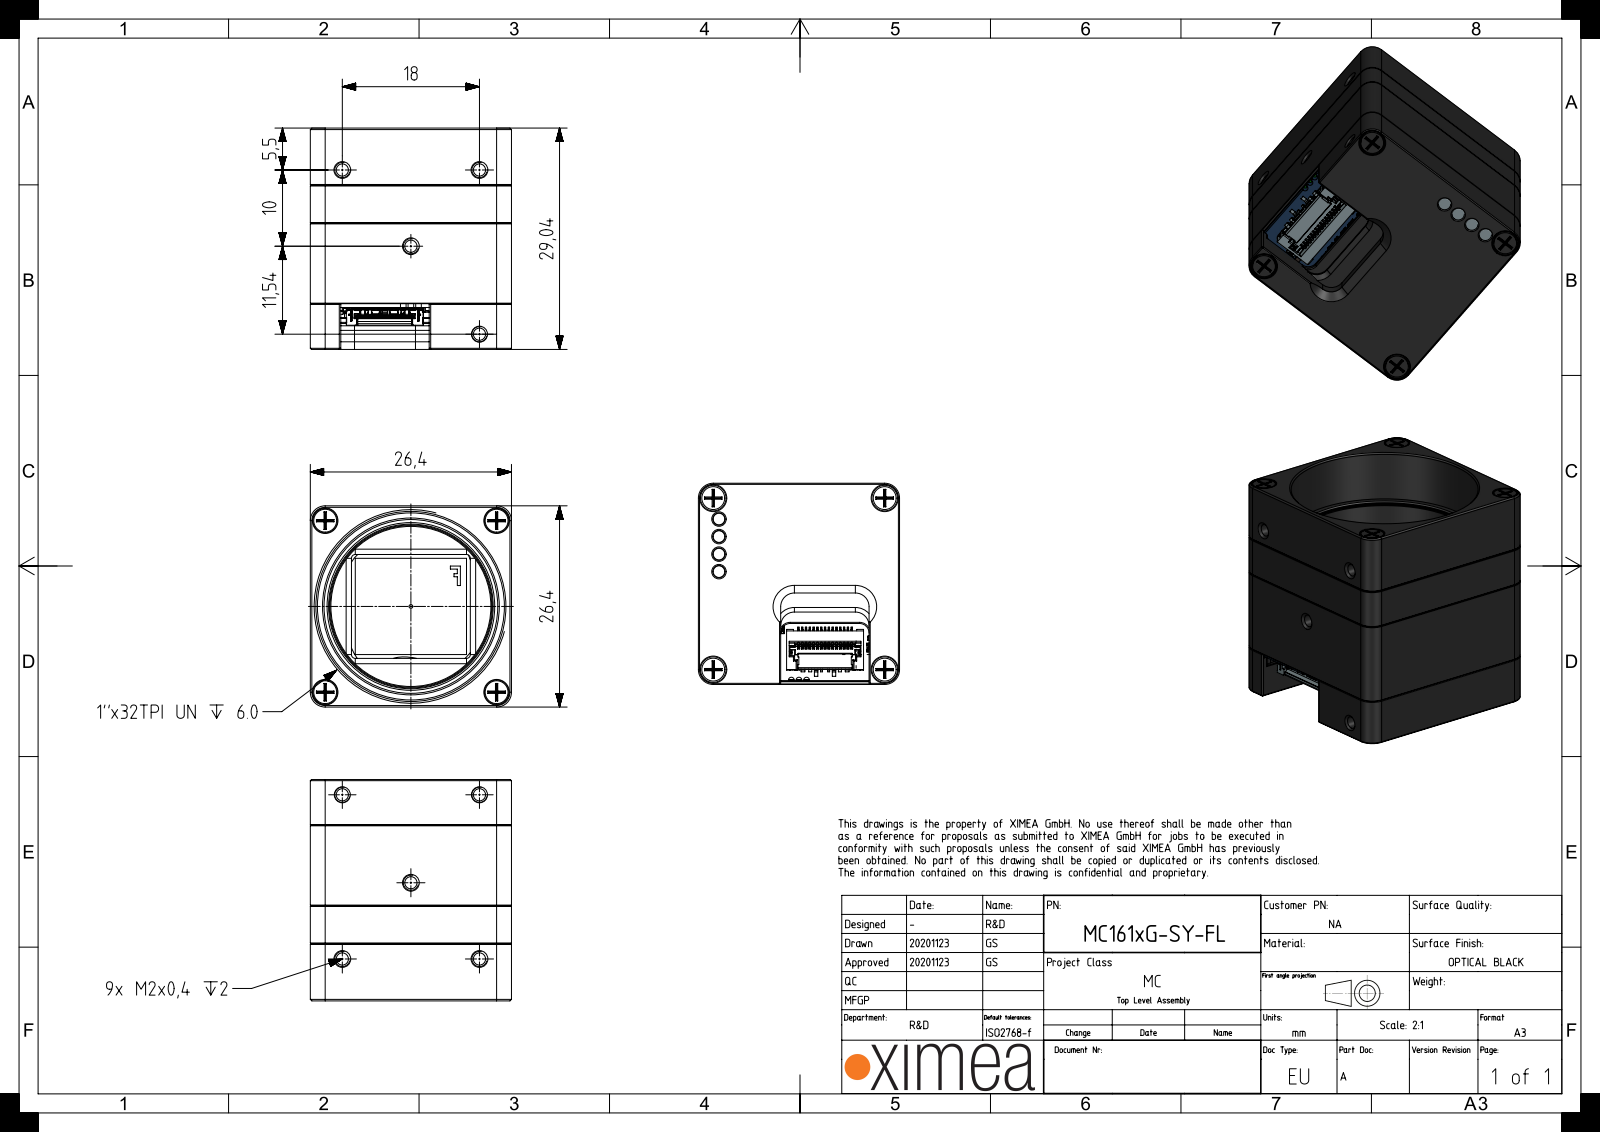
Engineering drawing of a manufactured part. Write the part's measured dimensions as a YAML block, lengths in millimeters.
part_name: "MT160xG-PR-SENSOR-PCA-LW; MECH-CB262-ANTIDUST-GSKT; MECH-O-RING-22X1-VI370; FLT-BK7-AR2X-D25 (+8 more)"
step_written_by: "SIEMENS PLM Software NX 1907 (AUTOMOTIVE_DESIGN)"
units: millimeters
bodies: {solids: 31, faces: 6735, planar: 4771, cylindrical: 1682, other: 282}
overall_size: [29, 26.4, 26.4]
volume: 9770
surface_area: 17190
round_holes:
  - {diameter: 1.6, count: 13}
  - {diameter: 1, count: 4}
  - {diameter: 2, count: 4}
  - {diameter: 2.1, count: 4}
  - {diameter: 3, count: 4}
  - {diameter: 3.2, count: 4}
  - {diameter: 3.4, count: 4}
  - {diameter: 1.3, count: 2}
  - {diameter: 1.7, count: 2}
  - {diameter: 4, count: 1}
  - {diameter: 21, count: 1}
  - {diameter: 22.8, count: 1}
round_bosses_or_shafts:
  - {diameter: 1.9, count: 4}
  - {diameter: 1.6, count: 4}
  - {diameter: 0.8, count: 4}
  - {diameter: 3, count: 2}
  - {diameter: 1.6, count: 2}
  - {diameter: 25, count: 1}
  - {diameter: 21.6, count: 1}
partial_cylinders:
  - {radius: 1, count: 24}
  - {radius: 0.4, count: 18}
  - {radius: 0.3, count: 17}
  - {radius: 0.2, count: 14}
  - {radius: 0.2, count: 12}
  - {radius: 0.5, count: 12}
  - {radius: 0.3, count: 8}
  - {radius: 1.3, count: 8}
face_to_face_distances: [26.4, 1, 11.6, 3.6, 8.1, 2.6, 10.6, 10.5, 4.6, 1]
hole_center_spacings: [15.9, 22.5, 2.3, 3.8, 4.6, 13.5, 13.5, 14.6]
